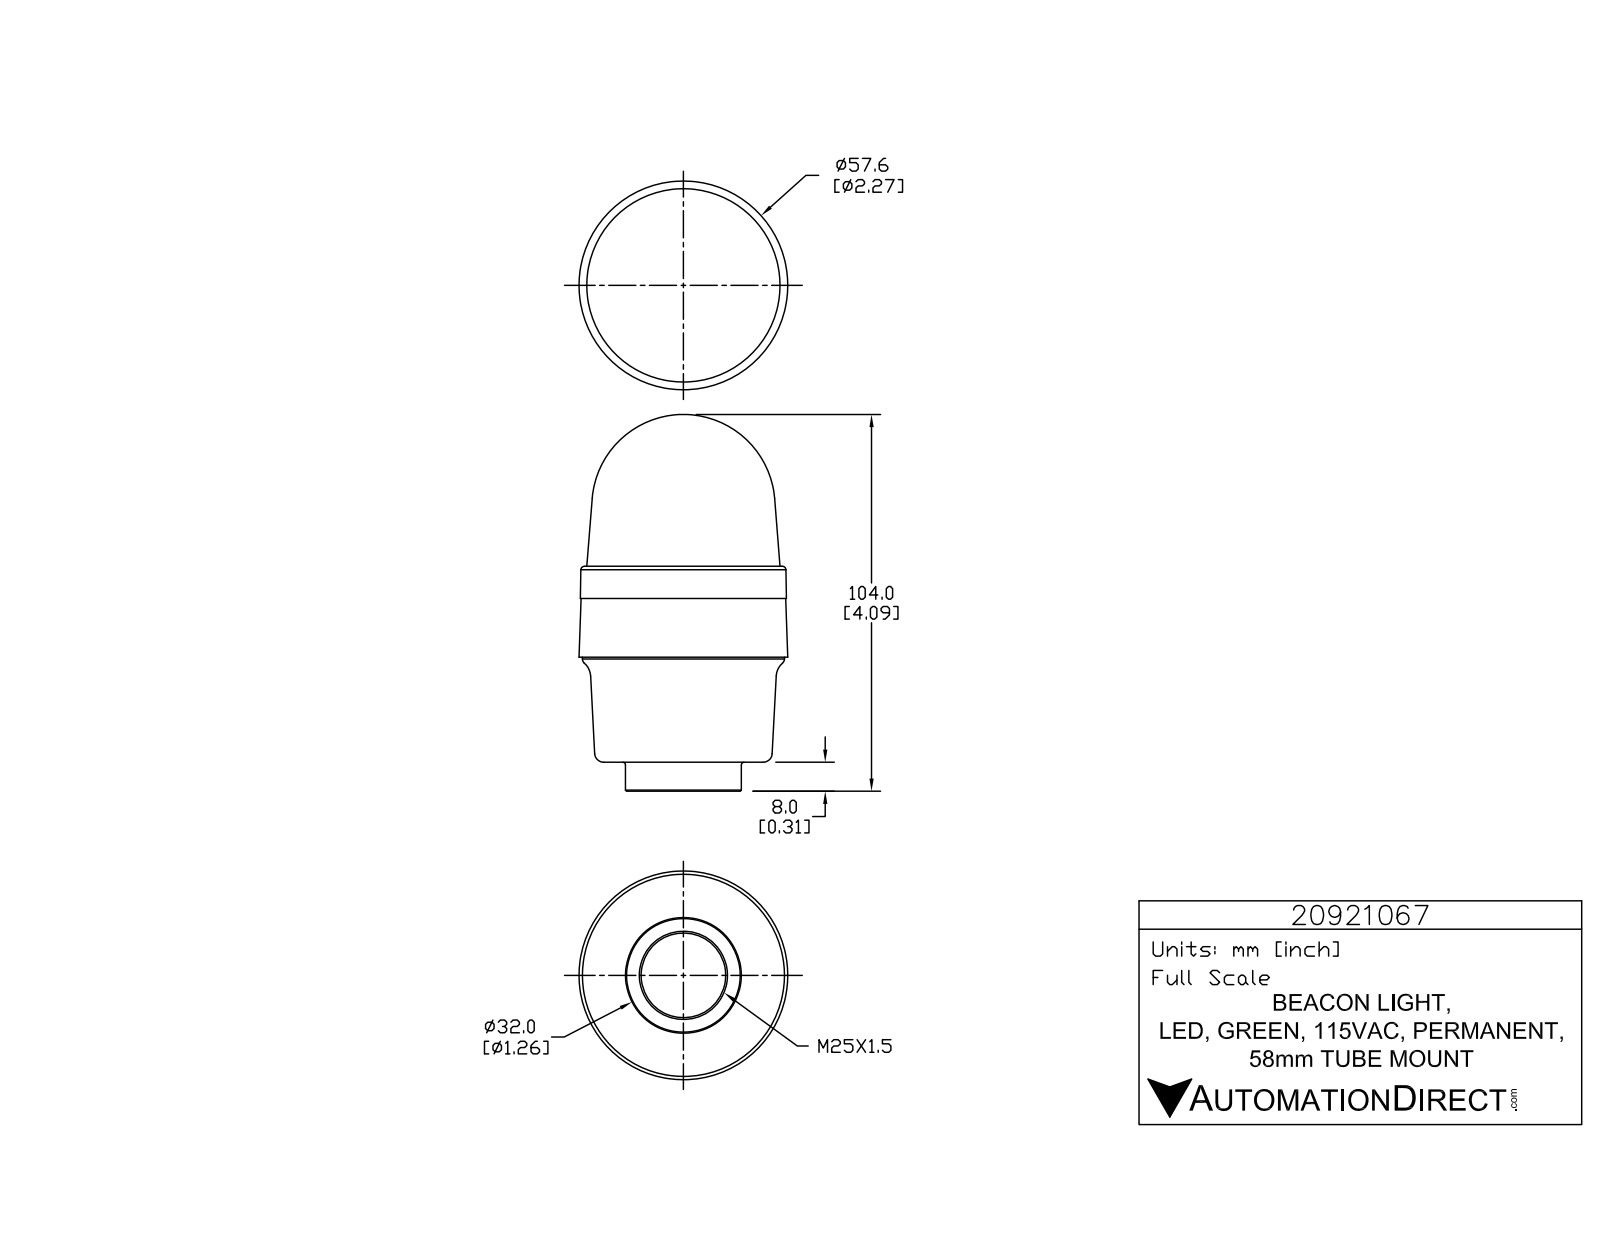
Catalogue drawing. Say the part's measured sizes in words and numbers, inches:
The part is named "20921067". Its 3-D file was written by "SolidWorks 2015 (AUTOMOTIVE_DESIGN)". It is 1 solid with 791 faces: 525 planar, 168 cylindrical and 98 other. Overall it measures 4.051 by 2.269 by 2.269 inches. Its volume is 11.72 cubic inches and its surface area 29.93 square inches. Round holes: 3 of diameter 0.039, 1 of diameter 0.92. Round bosses or shafts: 3 of diameter 0.226, 3 of diameter 0.056, 1 of diameter 2.197, 1 of diameter 1.26. Partial cylindrical surfaces (rounded edges, fillets, slot ends): 6 of radius 0.008, 6 of radius 0.008, 6 of radius 0.008, 6 of radius 0.131, 3 of radius 0.004, 3 of radius 0.005, 3 of radius 0.008, 3 of radius 0.008. The main face-to-face distances are 0.315, 1.142, 1.457, 0.988, 2.13, 2.445, 0.35, 0.638, 1.78, 2.094.
